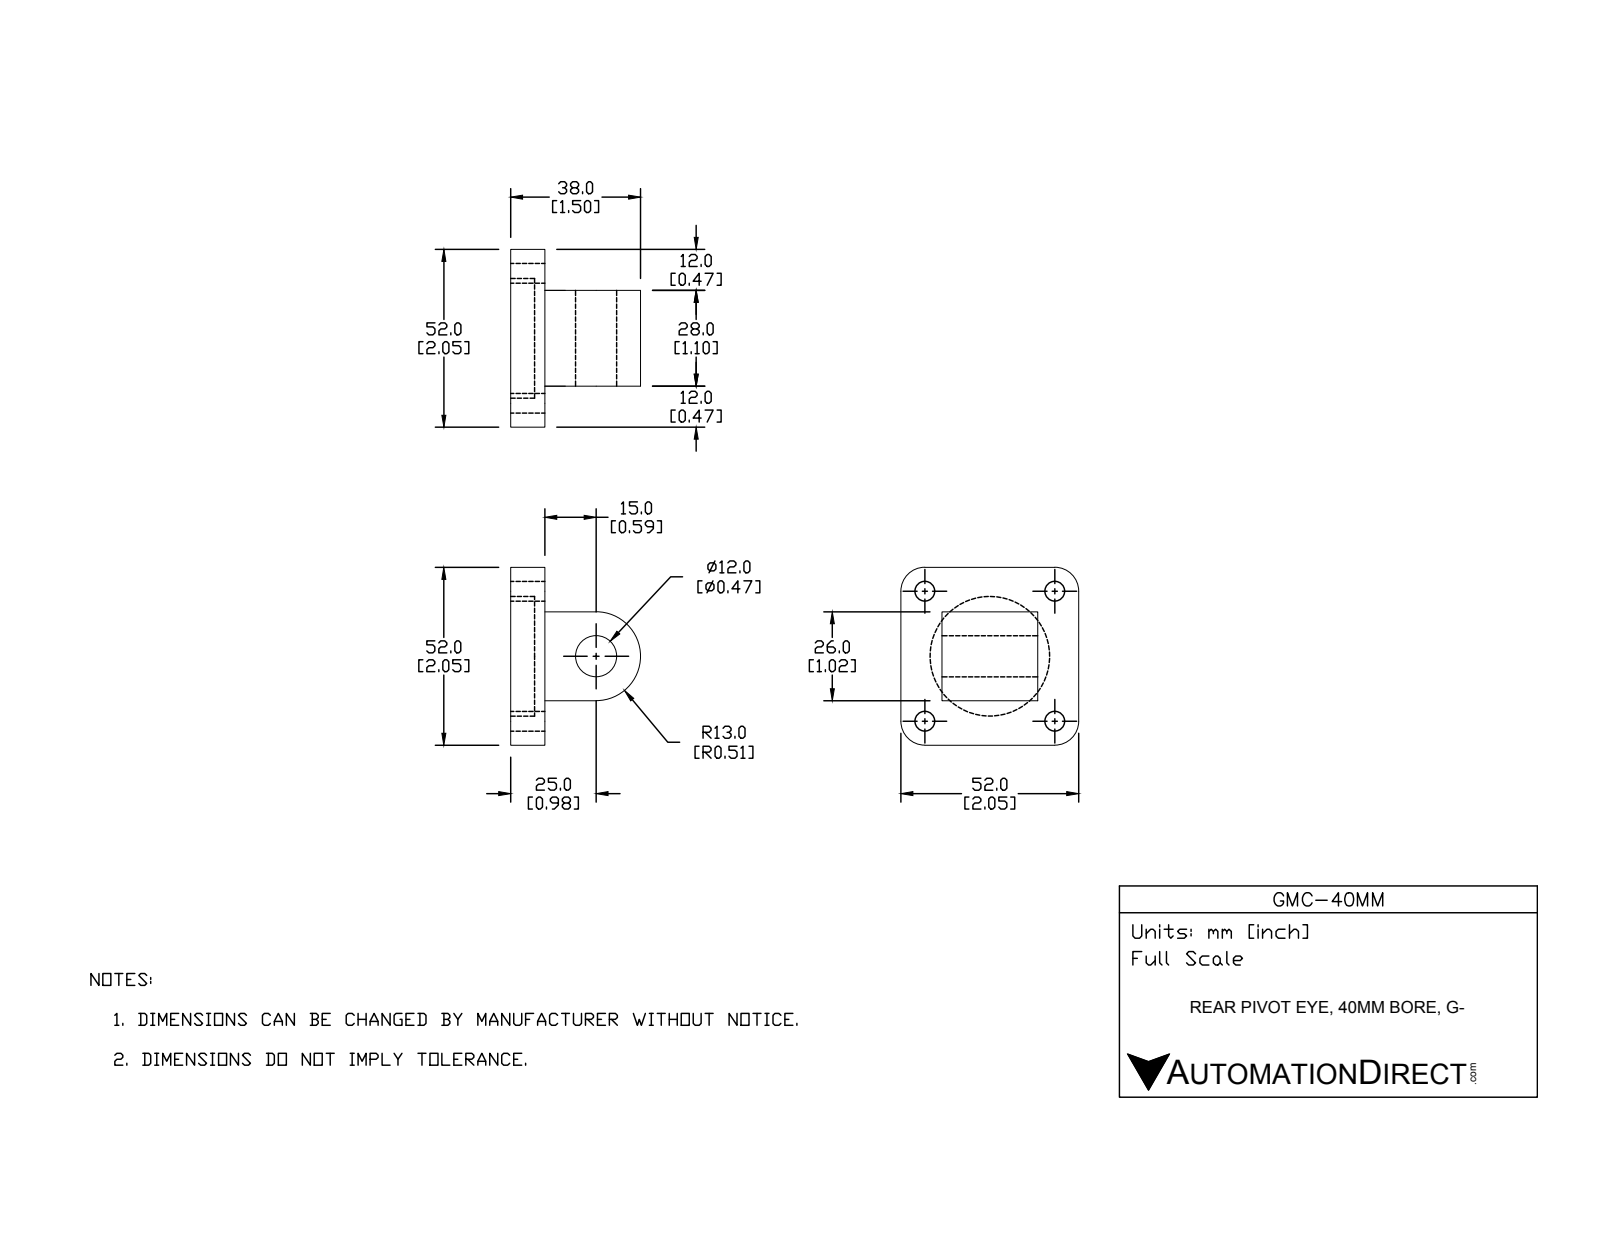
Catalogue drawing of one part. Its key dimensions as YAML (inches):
part_name: "GMC-40MM"
step_written_by: "SolidWorks 2017 (AUTOMOTIVE_DESIGN)"
units: inches
bodies: {solids: 1, faces: 28, planar: 11, cylindrical: 17, other: 0}
overall_size: [2.047, 2.047, 1.496]
volume: 2.076
surface_area: 18.55
round_holes:
  - {diameter: 0.228, count: 4}
  - {diameter: 0.472, count: 1}
  - {diameter: 1.378, count: 1}
partial_cylinders:
  - {radius: 0.276, count: 4}
  - {radius: 0.512, count: 1}
face_to_face_distances: [0.394, 0.276, 0.118, 0.512, 1.535, 2.047, 0.472, 1.575, 1.102, 1.024]
hole_center_spacings: [1.058, 1.496, 2.116]
